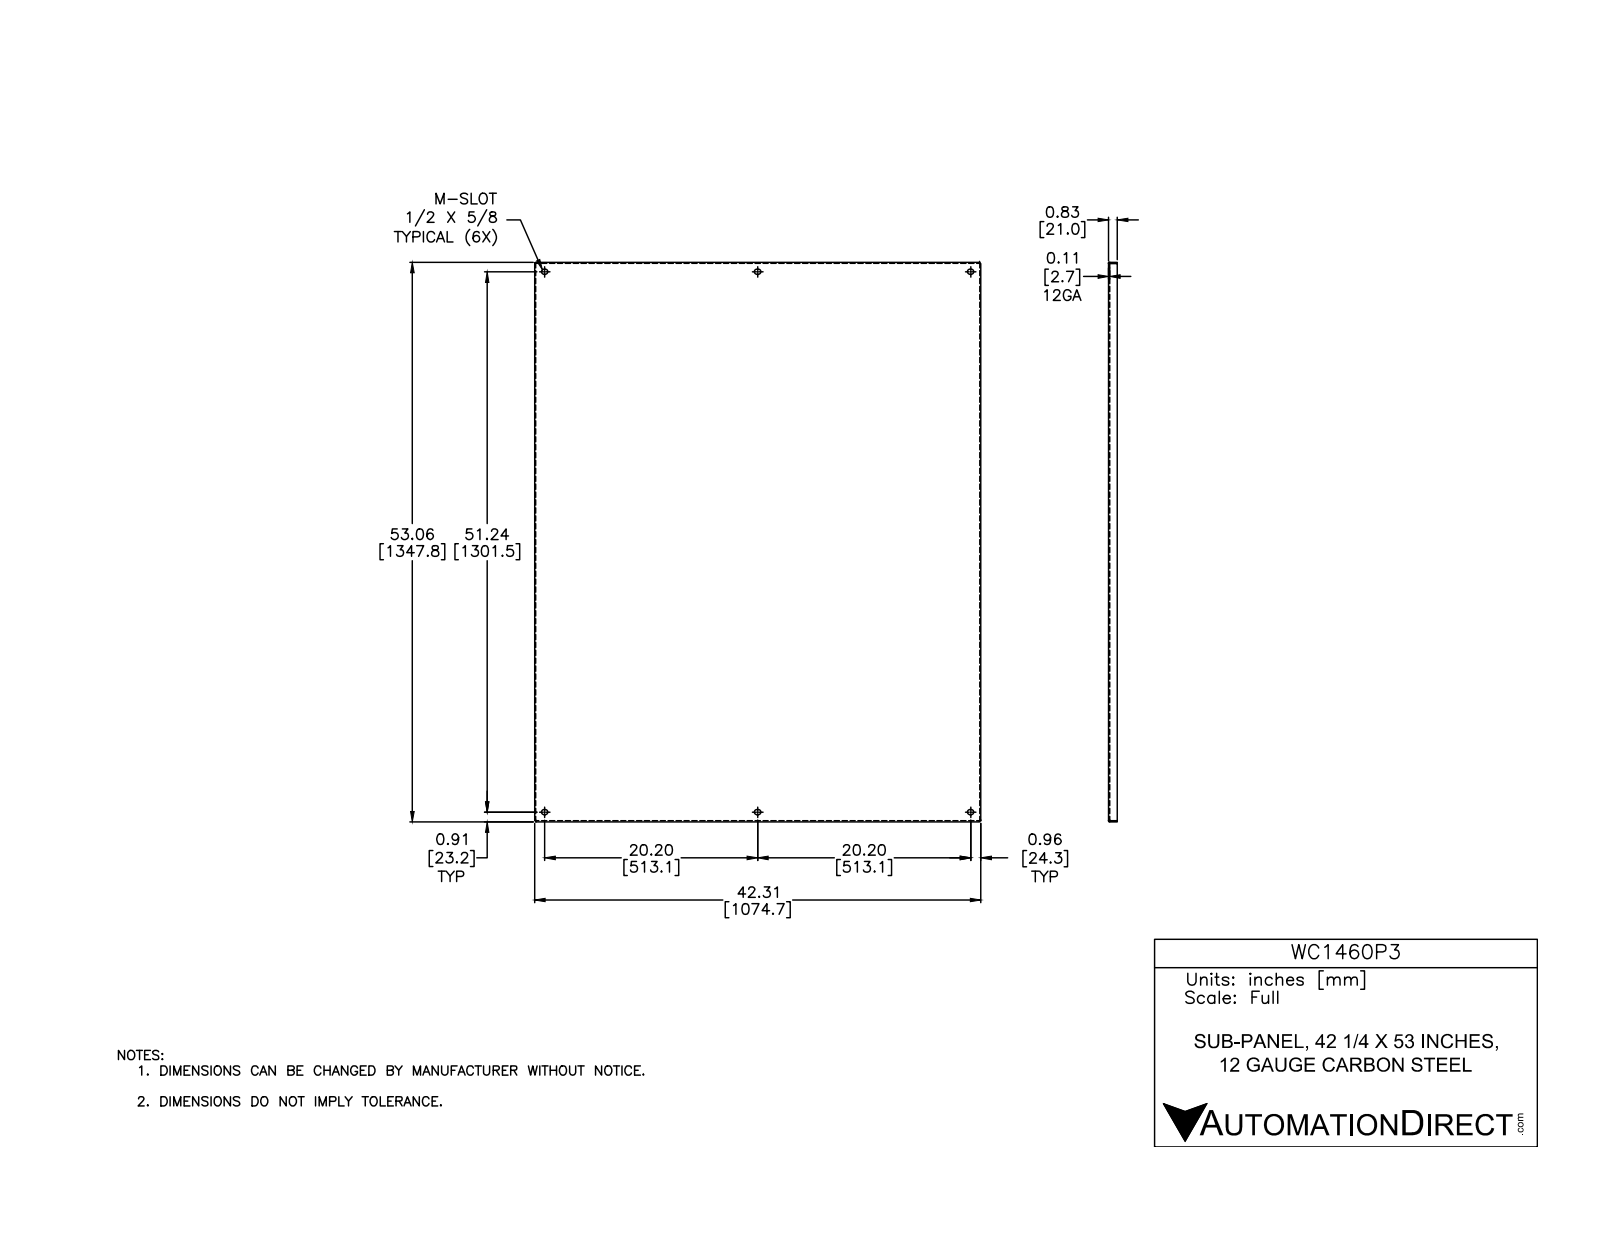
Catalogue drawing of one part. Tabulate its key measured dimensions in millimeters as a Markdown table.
| quantity | value |
| --- | --- |
| part name | WC1460P3 |
| STEP written by | SolidWorks 2014 (AUTOMOTIVE_DESIGN) |
| units | millimeters |
| bodies | 1 solid, 68 faces (34 planar, 26 cylindrical, 8 other) |
| overall size | 1347.8 × 1074.8 × 21 |
| volume | 4 074 000 mm³ |
| surface area | 3 081 000 mm² |
| partial cylindrical surfaces (radius × count) | 6.4 × 12, 2.7 × 3, 2.7 × 1 |
| main face-to-face distances | 2.7, 1072.1, 1345.1, 1074.8, 1069.4, 1347.8, 1342.5, 21, 18.4, 2.8 |
